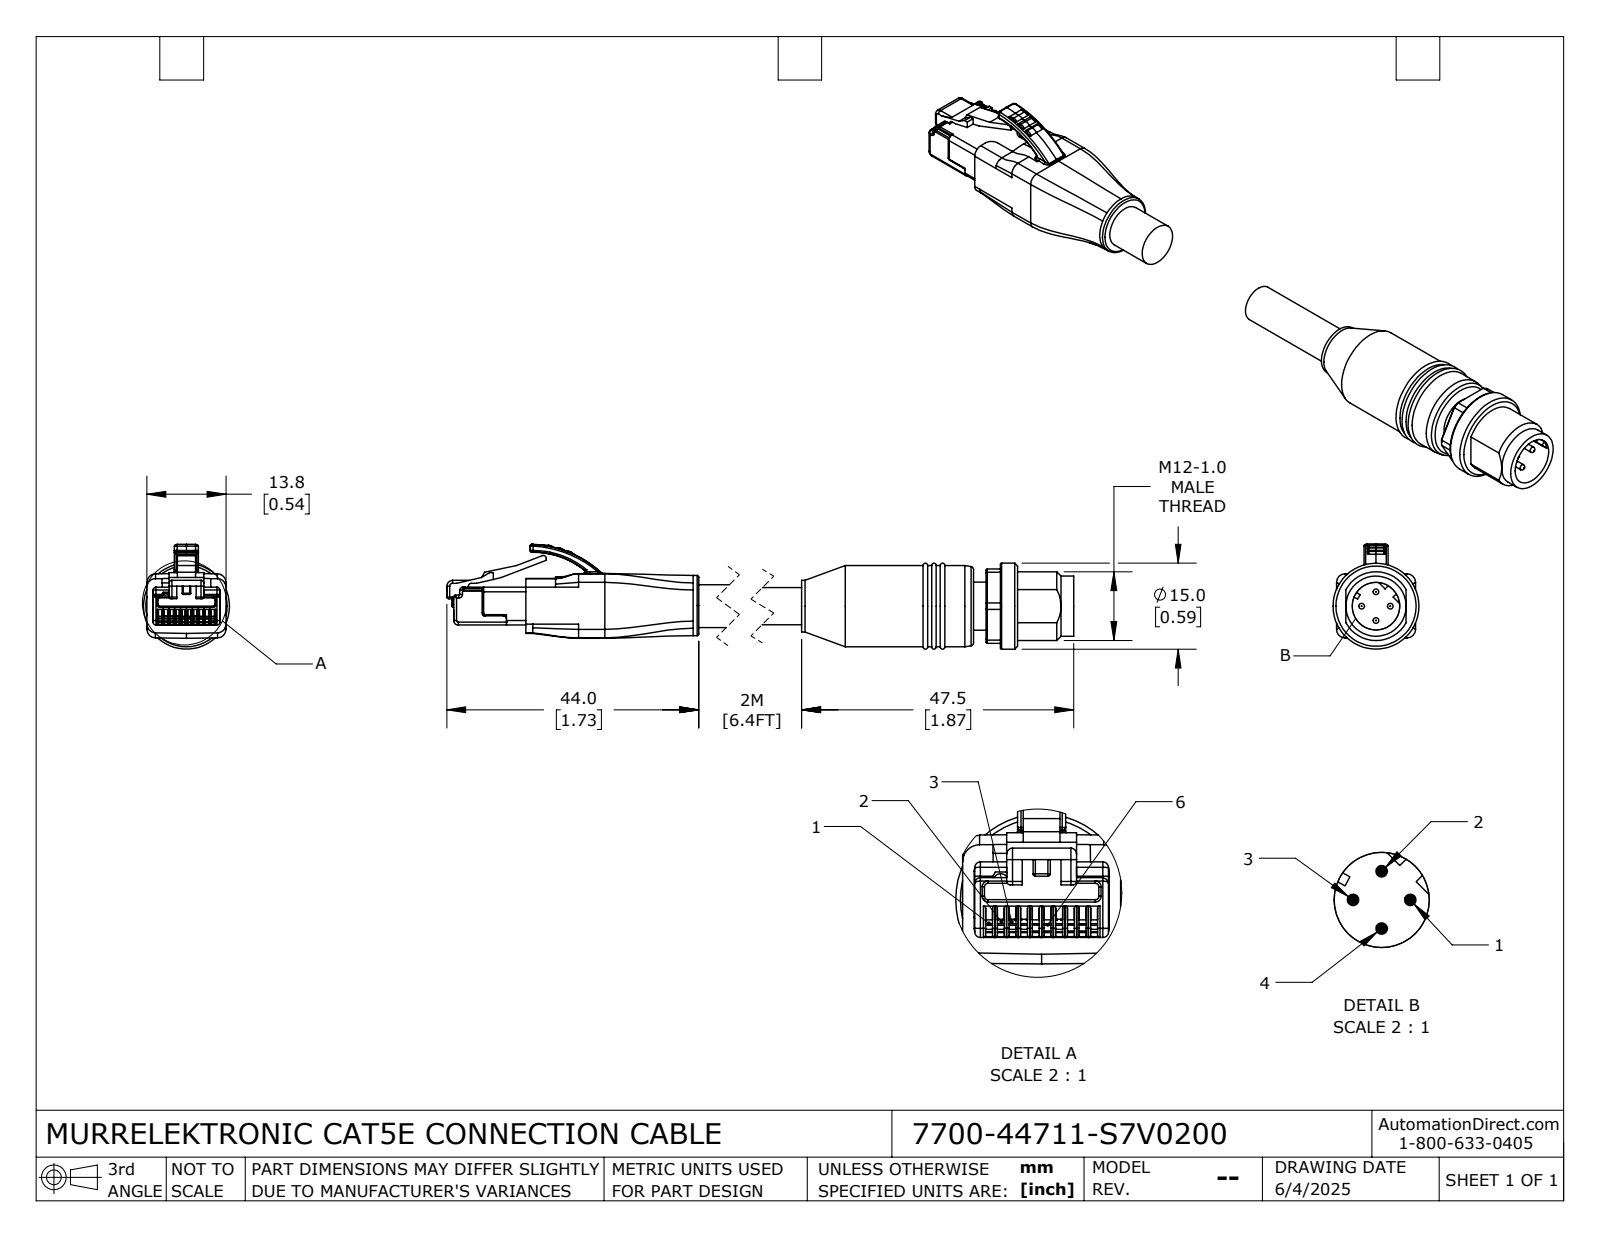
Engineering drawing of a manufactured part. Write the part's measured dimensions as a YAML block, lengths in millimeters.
part_name: "7700-44711-S7V0200_RJ45; 7700-44711-S7V0200_MALE; 7700-44711-S7V0200"
step_written_by: "SolidWorks 2024 (CONFIG_CONTROL_DESIGN)"
units: millimeters
bodies: {solids: 2, faces: 757, planar: 357, cylindrical: 235, other: 165}
overall_size: [144.5, 18.29, 15]
volume: 11873
surface_area: 5775
round_holes:
  - {diameter: 8.3, count: 1}
round_bosses_or_shafts:
  - {diameter: 1, count: 4}
  - {diameter: 10.5, count: 2}
  - {diameter: 15, count: 1}
  - {diameter: 14.2, count: 1}
  - {diameter: 9, count: 1}
  - {diameter: 8.4, count: 1}
  - {diameter: 7.5, count: 1}
  - {diameter: 6.5, count: 1}
partial_cylinders:
  - {radius: 0.2, count: 61}
  - {radius: 0.5, count: 25}
  - {radius: 0.3, count: 14}
  - {radius: 1.5, count: 9}
  - {radius: 0.8, count: 5}
  - {radius: 0.54, count: 2}
  - {radius: 5, count: 2}
  - {radius: 0.13, count: 1}
face_to_face_distances: [13.8, 2.2, 1.65, 12.15, 1.01, 12.79, 0.64, 11.14, 9.8, 0.9]
